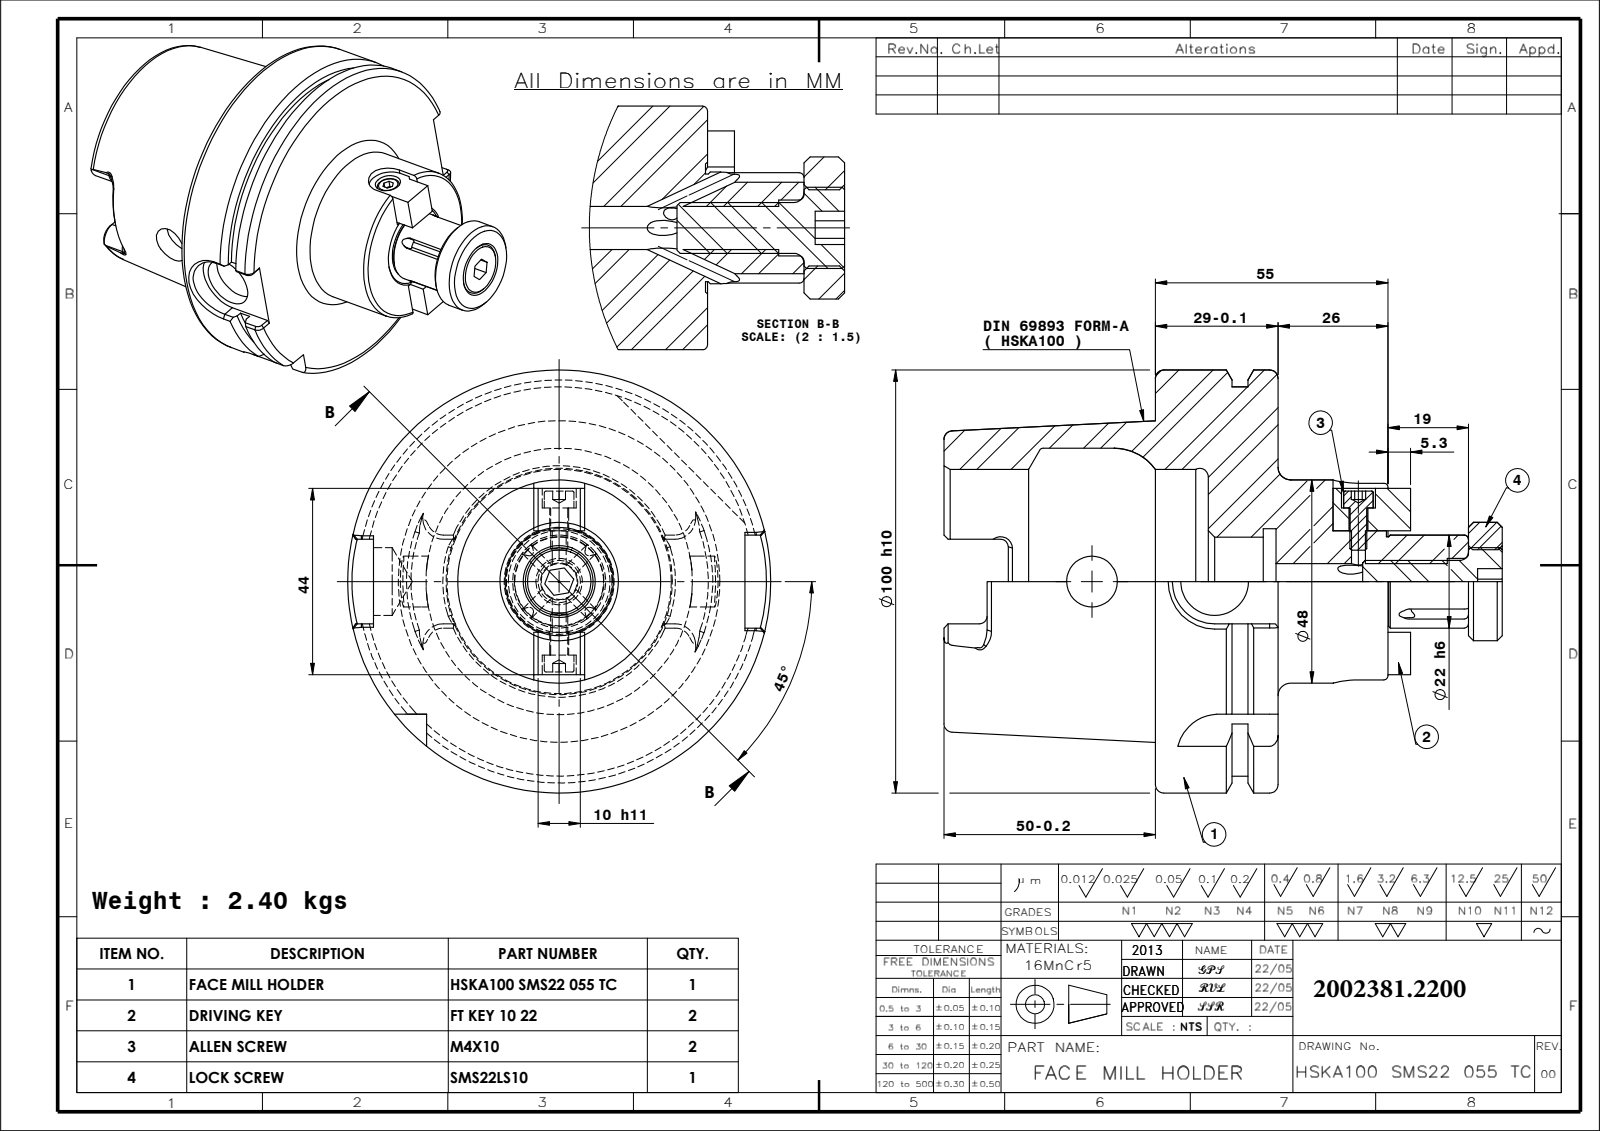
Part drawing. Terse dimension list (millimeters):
name: SMS22LS10; SMS22LS10-2; HSKA100 SMS22 055 TC; SMS22LS10-1 (+2 more)
written by: SolidWorks 2009 (CONFIG_CONTROL_DESIGN)
unit: mm
bodies: 7 solids, 347 faces (132 planar, 98 cylindrical, 117 other)
size: 132 × 100 × 100
volume: 310 984 mm³; area: 63 200 mm²
holes: 4× ⌀3, 1× ⌀3.3, 1× ⌀4.5, 1× ⌀8, 1× ⌀8.5, 1× ⌀11, 1× ⌀12, 1× ⌀15, 1× ⌀16, 1× ⌀21, 1× ⌀25, 1× ⌀53
bosses: 1× ⌀100, 1× ⌀92, 1× ⌀48, 1× ⌀28, 1× ⌀22, 1× ⌀21.2, 1× ⌀16, 1× ⌀10
rounds: 6× R1.8, 4× R1, 4× R4.88, 2× R10, 1× R6, 1× R11
face distances: 29, 12.5, 16.5, 50, 62.5, 79, 105, 55, 42.5, 26
hole spacings: 29
